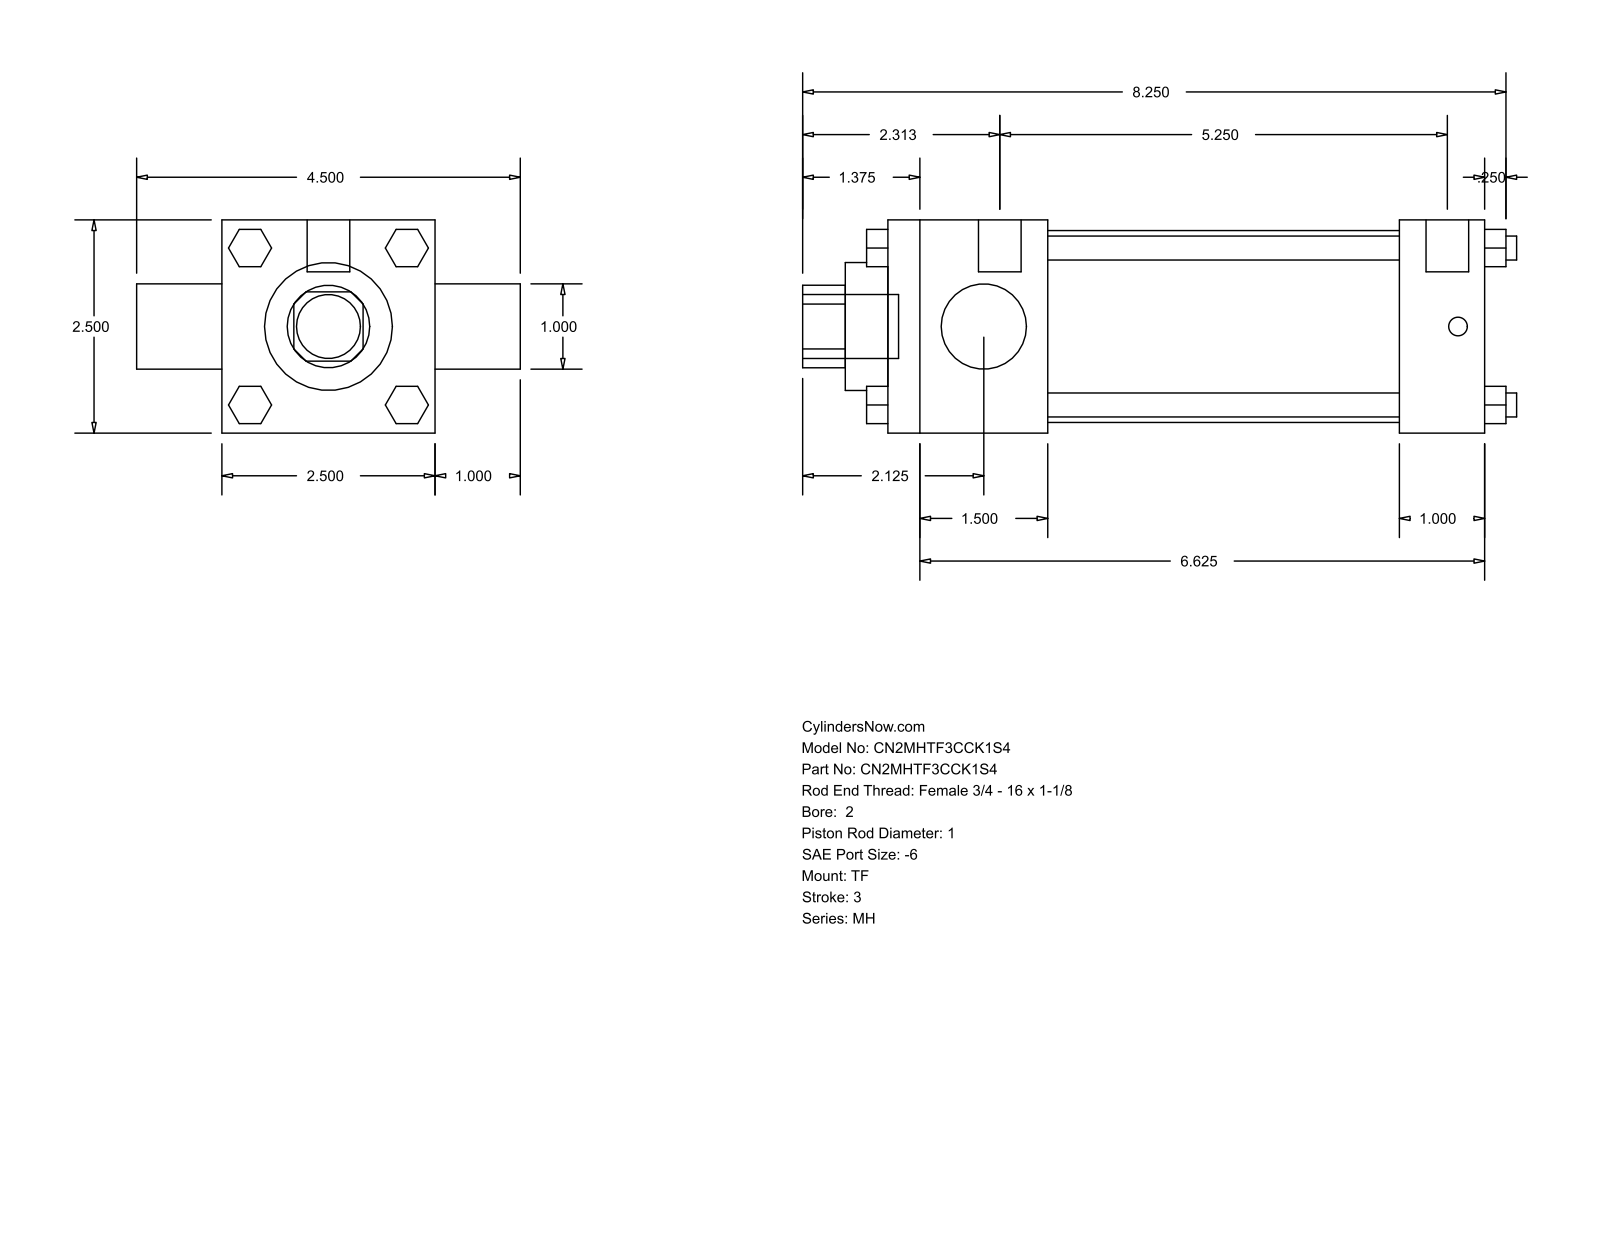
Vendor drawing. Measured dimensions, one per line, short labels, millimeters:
name: MH_TF__0200_1
written by: GSSL Pune (CONFIG_CONTROL_DESIGN)
unit: mm
bodies: 0 solids, 120 faces (92 planar, 28 cylindrical, 0 other)
size: 212.72 × 114.3 × 63.5
holes: 2× ⌀25.4, 1× ⌀38.1, 1× ⌀57.15
bosses: 4× ⌀7.14, 3× ⌀5.56, 2× ⌀12.7, 1× ⌀19.05
rounds: 1× R12.29
face distances: 63.5, 177.8, 25.4, 47.63, 152.4, 104.77, 130.17, 88.9, 190.5, 6.35
